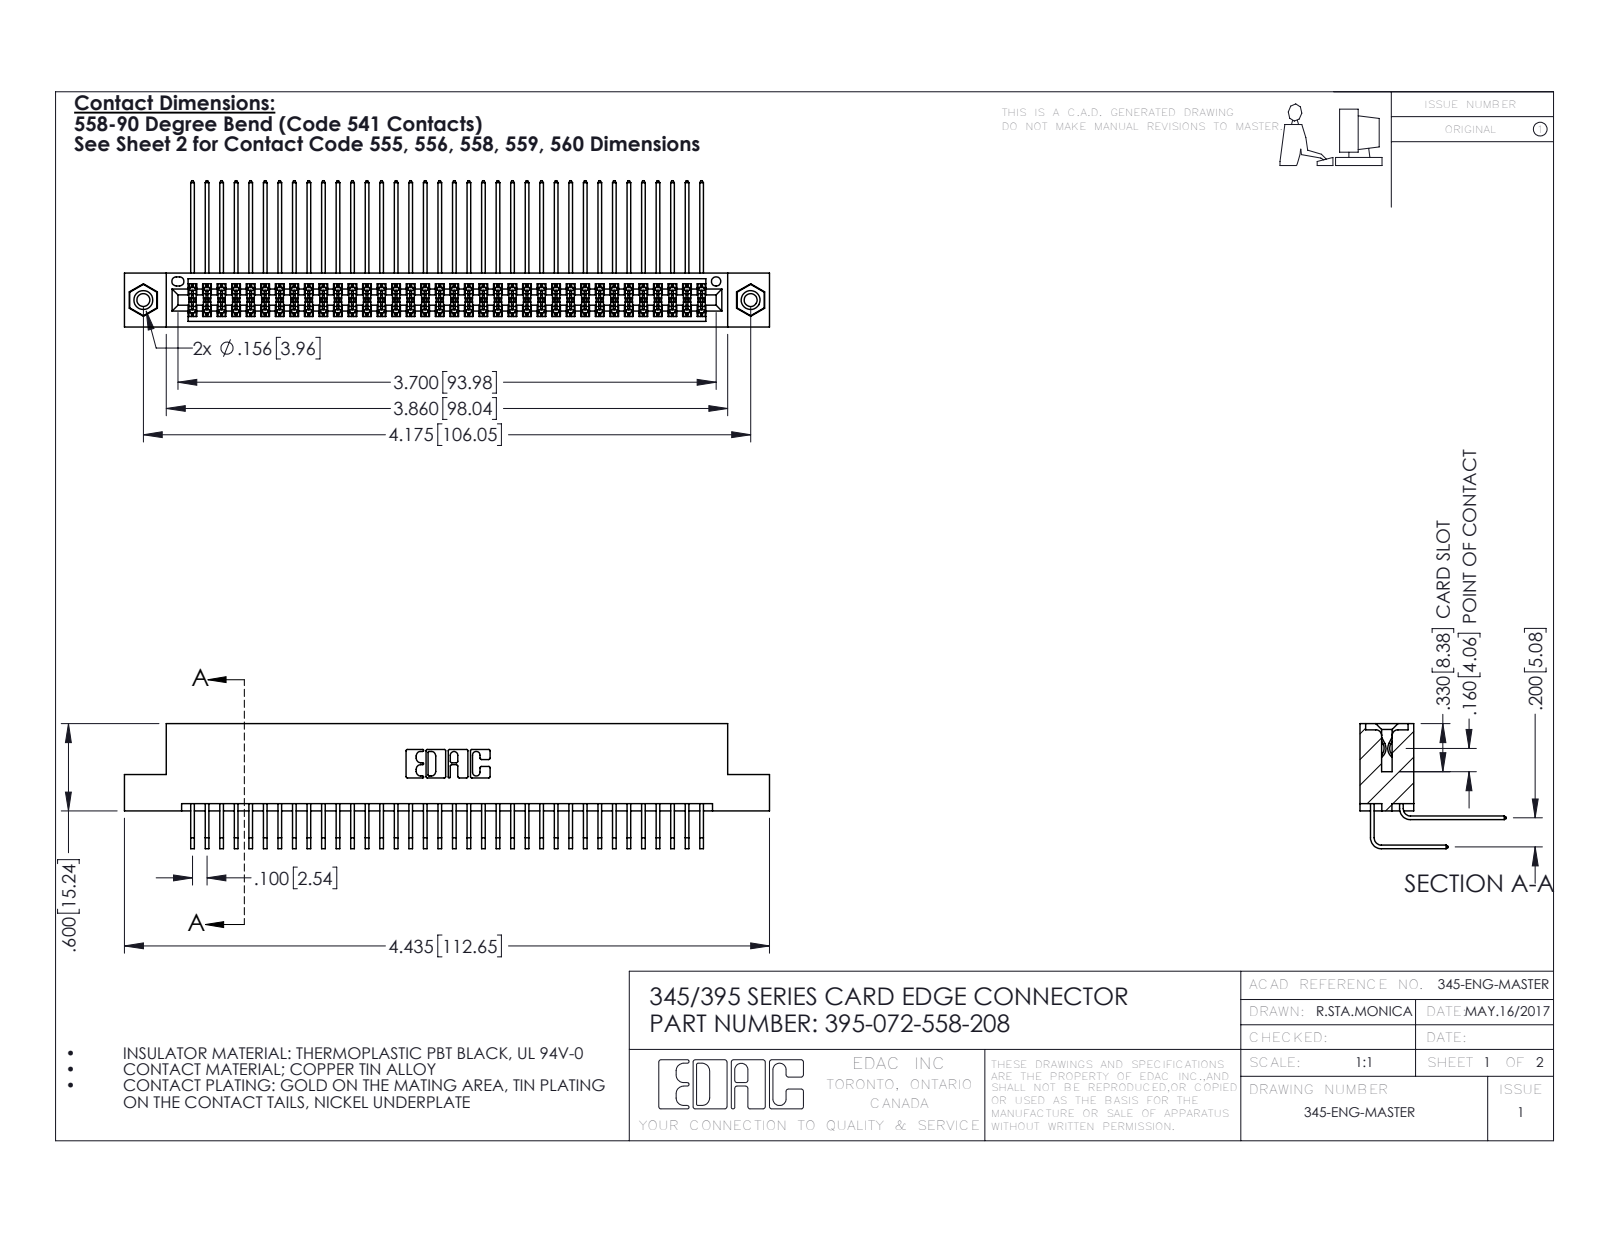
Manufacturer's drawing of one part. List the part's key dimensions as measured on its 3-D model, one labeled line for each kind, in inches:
Part name (STEP PRODUCT): 345 Part_Flush Mounting Lugs - 0.156 Dia-TI; 395-072-558-208; 345-292-001_558 559 Tail - 1; 345-292-001_558 Tail - 2 (+1 more)
STEP written by: SolidWorks 2016 (CONFIG_CONTROL_DESIGN)
Units: inches
Bodies: 75 solids, 3930 faces (2632 planar, 1282 cylindrical, 16 other)
Overall size (bounding box): 4.435 × 1.005 × 0.859
Volume: 0.689 in³ · Surface area: 28.75 in²
Round holes (diameter × count): ⌀0.089 ×2, ⌀0.125 ×2, ⌀0.156 ×2, ⌀0.064 ×1
Round bosses / shafts (diameter × count): ⌀0.155 ×2
Partial cylindrical surfaces — rounded edges, fillets, slot ends (radius × count): R0.006 ×109, R0.01 ×22, R0.007 ×6, R0.031 ×6, R0.026 ×3, R0.014 ×2, R0.019 ×2, R0.022 ×2
Main face-to-face distances: 0.072, 0.298, 0.2, 0.37, 0.098, 0.272, 0.025, 0.225, 0.025, 0.175
Hole centre spacings: 0.27, 3.939, 4.175
